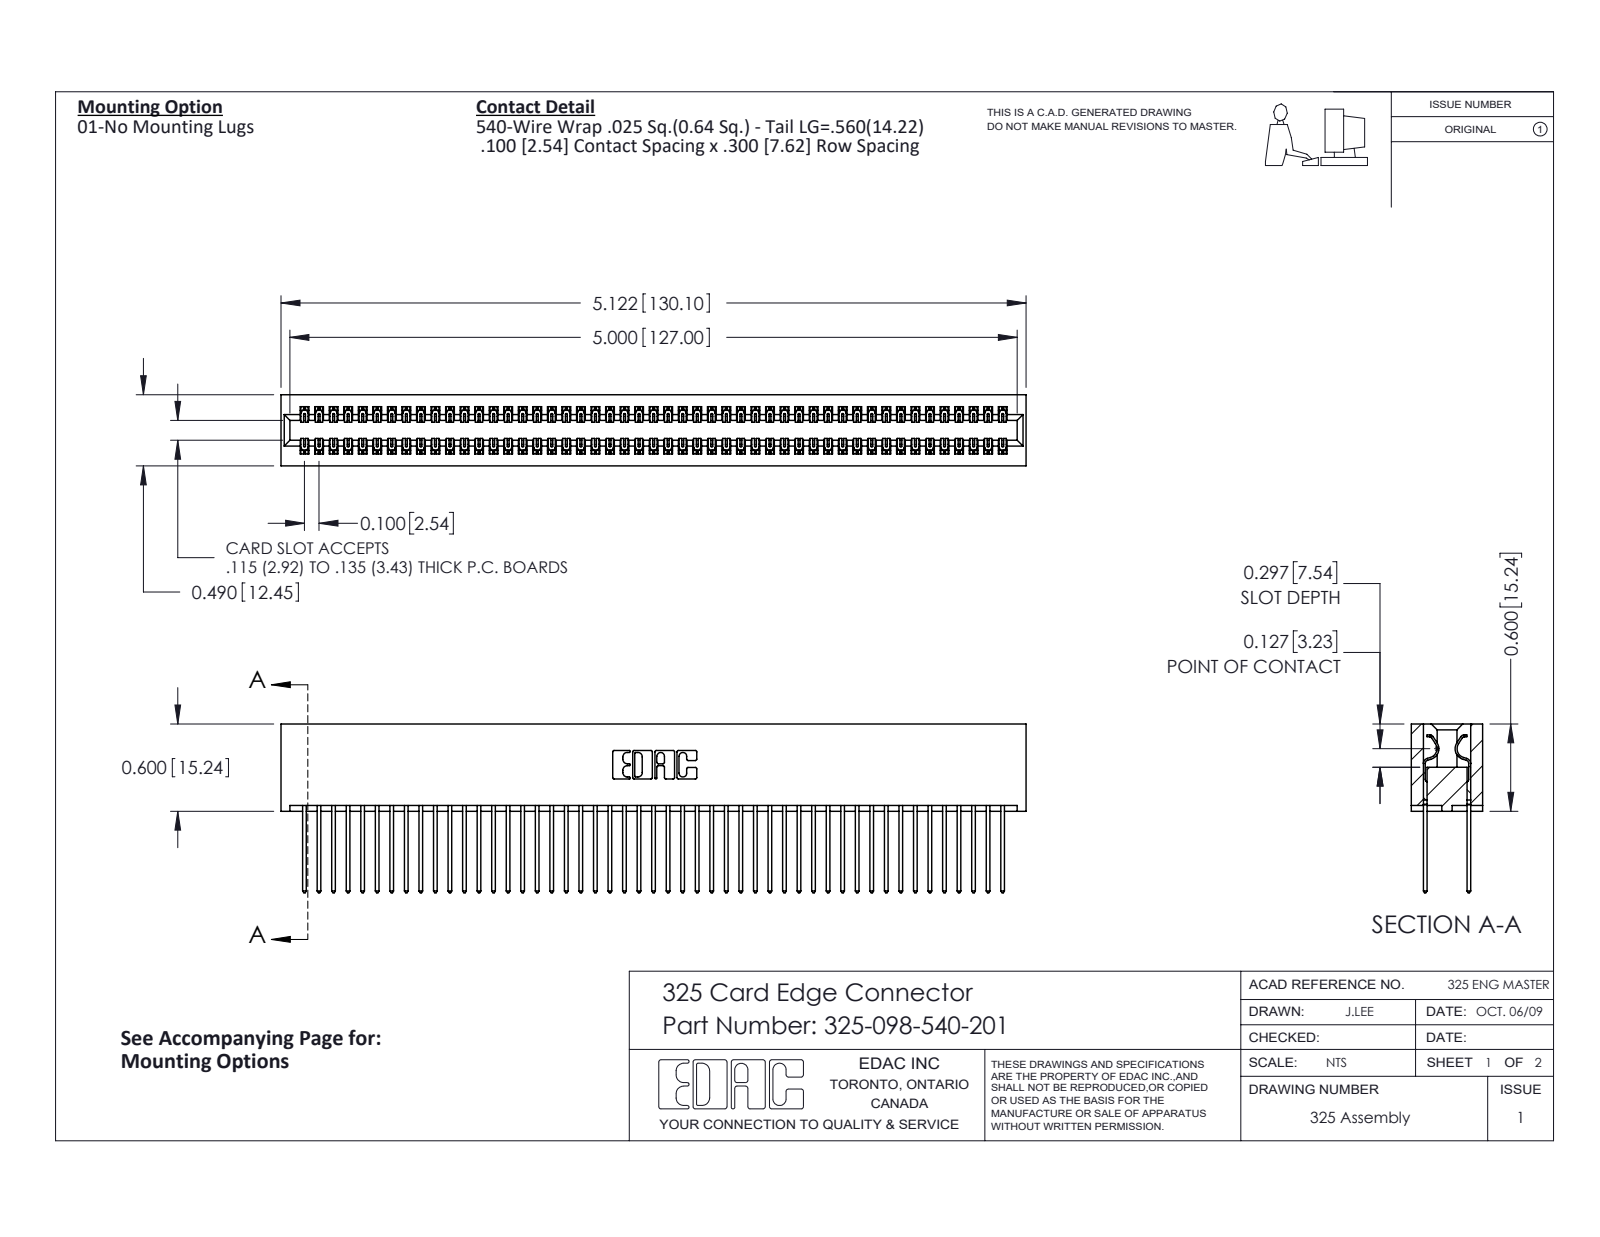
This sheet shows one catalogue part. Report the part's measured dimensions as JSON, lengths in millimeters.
{"part_name": "325 Part_Lugless; 325-292-001_325-293-140; 325-098-540-201", "step_written_by": "SolidWorks 2016 (CONFIG_CONTROL_DESIGN)", "units": "millimeters", "bodies": {"solids": 99, "faces": 5202, "planar": 3594, "cylindrical": 1608, "other": 0}, "overall_size": [130.1, 29.5, 12.4], "volume_mm3": 17830, "surface_area_mm2": 24180, "partial_cylinders_radius": [[0.2, 147], [0.3, 98], [0.3, 22], [0.2, 6], [0.8, 6], [0.7, 3], [0.4, 2], [0.6, 2]], "face_to_face_distances": [2.1, 10.3, 7.6, 2.7, 9.7, 0.6, 8.3, 12.4, 7, 14.2]}
